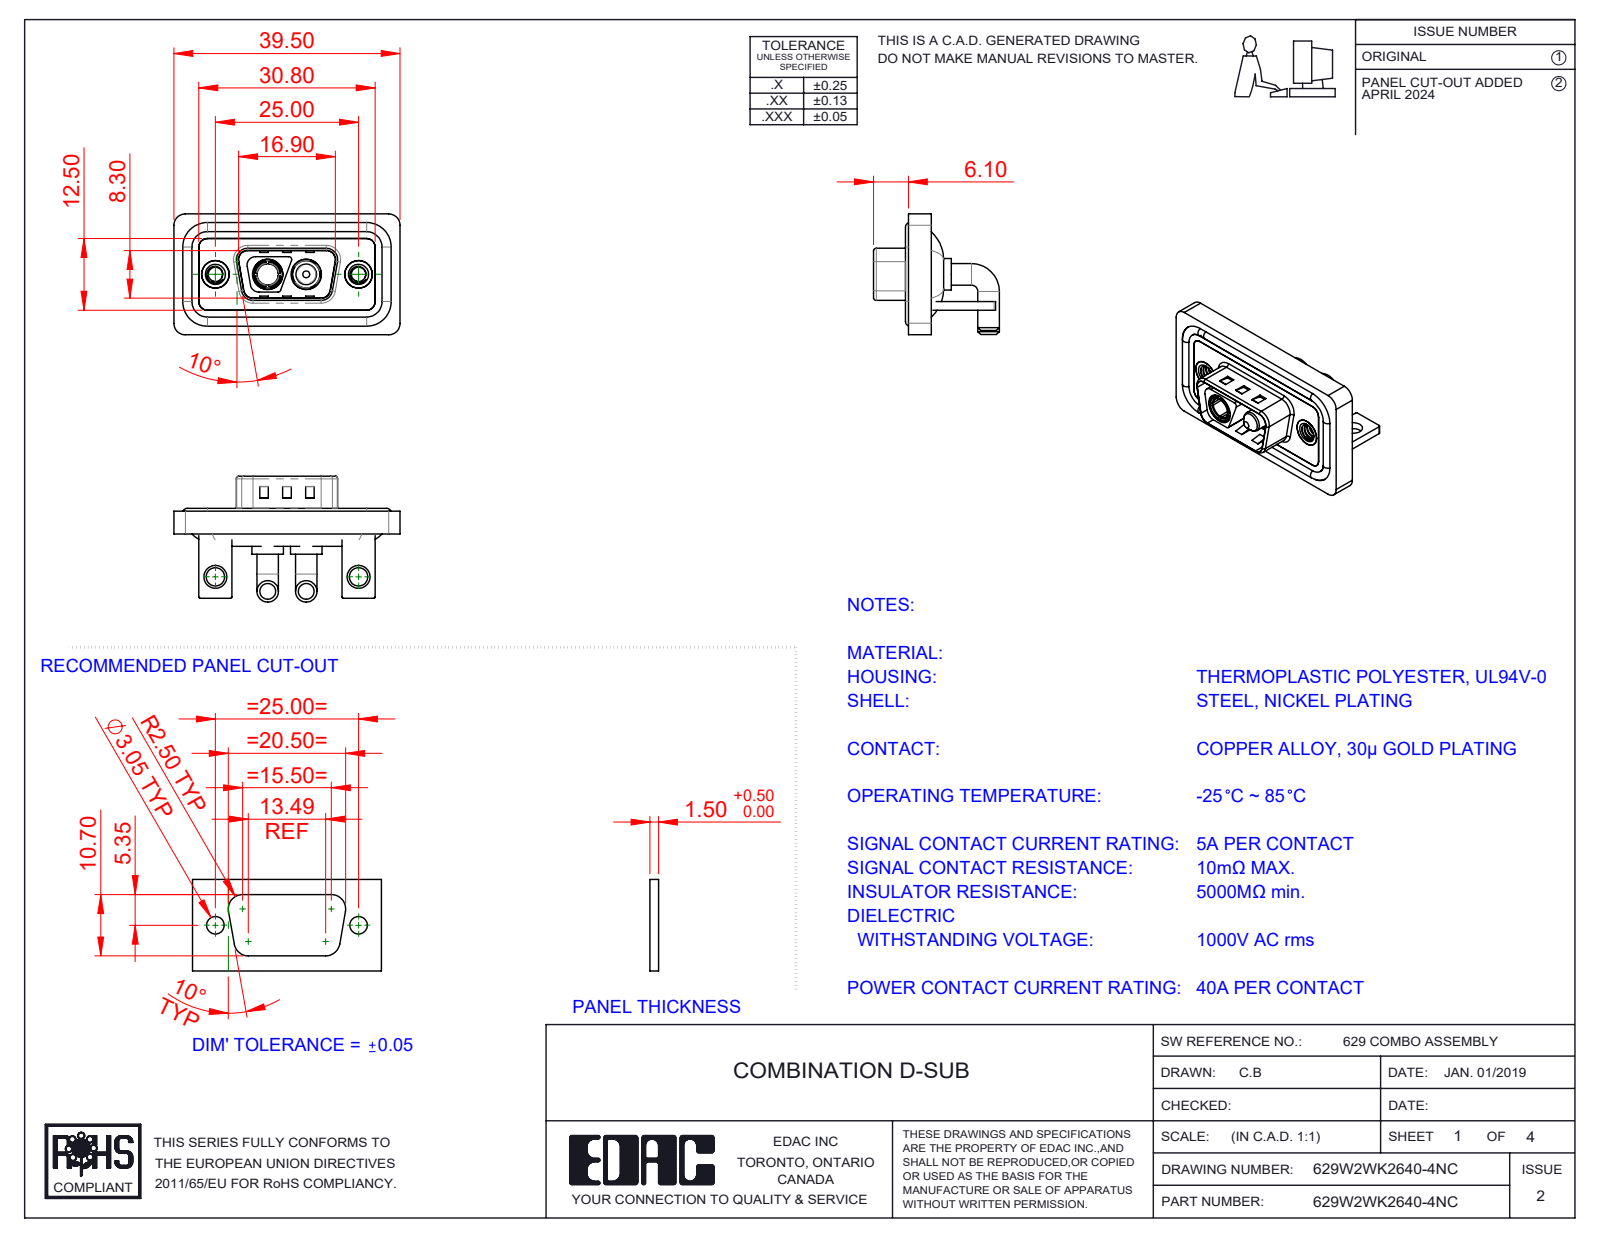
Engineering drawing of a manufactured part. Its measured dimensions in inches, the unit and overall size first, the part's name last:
Units: inches
Overall size (bounding box): 1.555 × 0.865 × 0.831
Round holes (diameter × count): ⌀0.098 ×2, ⌀0.126 ×2, ⌀0.157 ×2, ⌀0.189 ×2, ⌀0.191 ×2, ⌀0.197 ×2, ⌀0.209 ×2, ⌀0.146 ×1
Round bosses / shafts (diameter × count): ⌀0.148 ×4, ⌀0.063 ×4, ⌀0.217 ×2, ⌀0.205 ×2, ⌀0.193 ×2, ⌀0.187 ×2, ⌀0.195 ×1, ⌀0.142 ×1
Partial cylindrical surfaces — rounded edges, fillets, slot ends (radius × count): R0.059 ×20, R0.079 ×19, R0.01 ×16, R0.02 ×11, R0.063 ×8, R0.024 ×4, R0.026 ×4, R0.035 ×4
Main face-to-face distances: 0.016, 0.059, 0.114, 0.031, 0.043, 0.047, 0.083, 0.063, 0.146, 0.098
Hole centre spacings: 0.36, 0.624, 0.984, 0.265
Volume: 0.311 in³ · Surface area: 12.73 in²
Bodies: 13 solids, 580 faces (209 planar, 249 cylindrical, 122 other)
Part name (STEP PRODUCT): 629Combo Housing_2WK2; Power Socket_40A RA; 629Combo Threaded Rivet_B; Power Pin_40A RA (+5 more)
STEP written by: SolidWorks 2023 (CONFIG_CONTROL_DESIGN)
